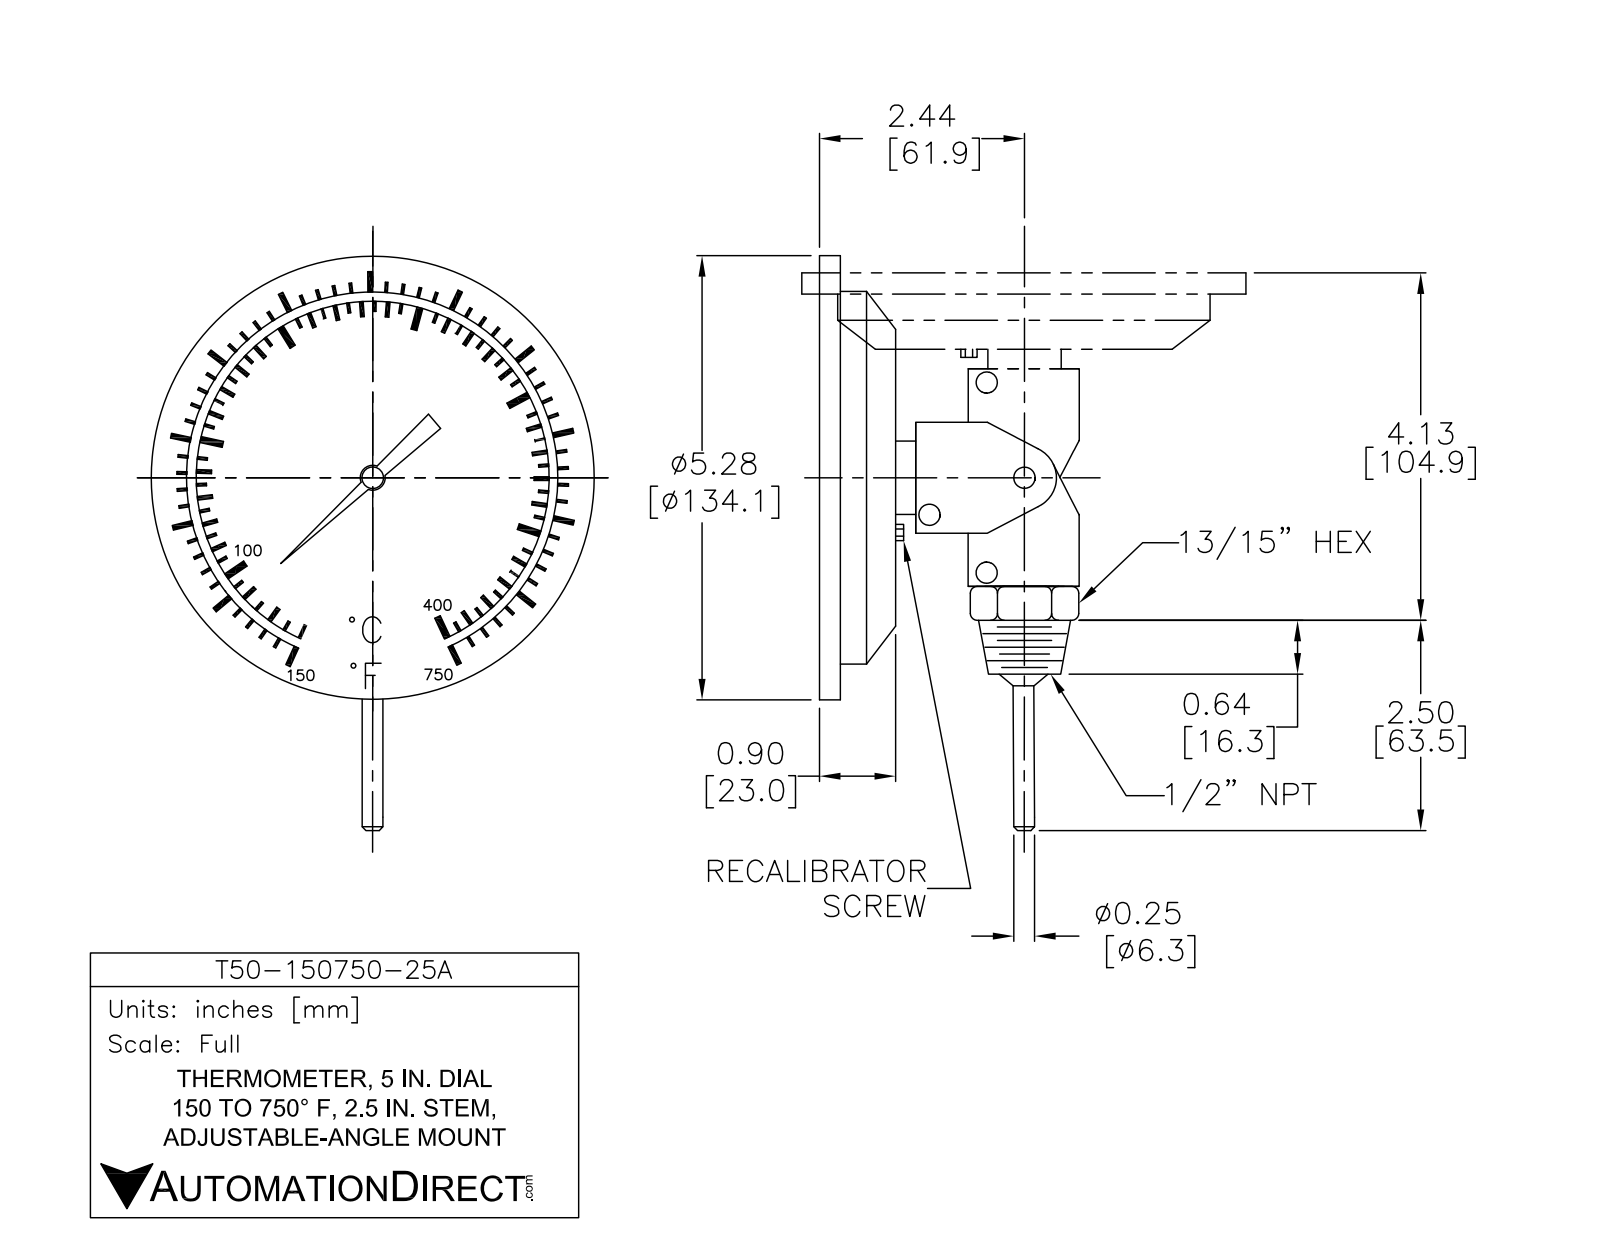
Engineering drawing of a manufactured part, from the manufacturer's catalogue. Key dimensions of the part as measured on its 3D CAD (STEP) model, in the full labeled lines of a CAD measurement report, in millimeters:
Part name (STEP PRODUCT): T50-150750-25A
STEP written by: SolidWorks 2021 (AUTOMOTIVE_DESIGN)
Units: millimetres
Bodies: 1 solid, 513 faces (305 planar, 45 cylindrical, 163 other)
Overall size (bounding box): 164.1 × 134.1 × 134.1
Volume: 164 900 mm³ · Surface area: 61 690 mm²
Round holes (diameter × count): ⌀87 ×1, ⌀94.1 ×1, ⌀120.9 ×1, ⌀122.8 ×1
Round bosses / shafts (diameter × count): ⌀7.7 ×4, ⌀3.7 ×2, ⌀134.1 ×1, ⌀126.2 ×1, ⌀87.7 ×1, ⌀21.6 ×1, ⌀20.9 ×1, ⌀13.8 ×1
Partial cylindrical surfaces — rounded edges, fillets, slot ends (radius × count): R1.5 ×10, R1 ×4, R4.3 ×1, R8.5 ×1, R8.5 ×1, R8.7 ×1, R10.2 ×1, R47.4 ×1
Main face-to-face distances: 9, 1.9, 1.4, 10.8, 30.2, 20.7, 11.7, 9.9, 31.6, 61.8
